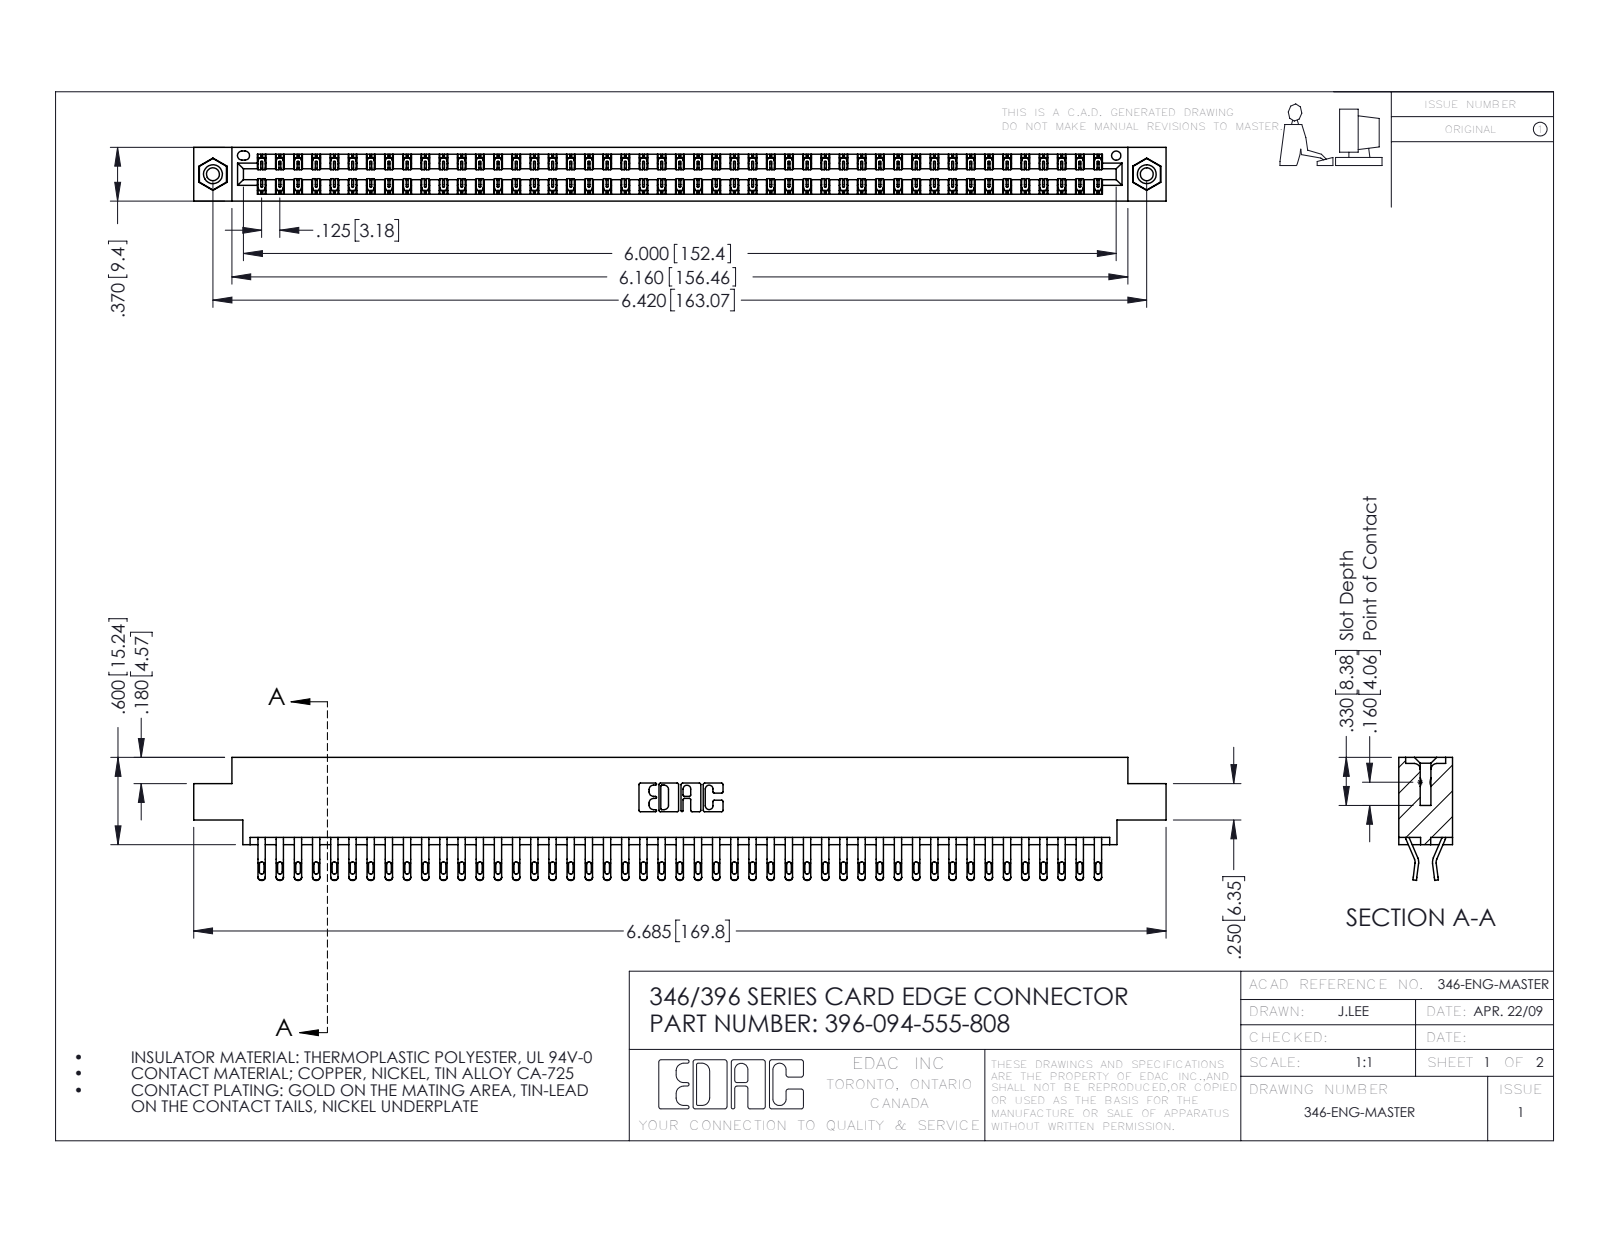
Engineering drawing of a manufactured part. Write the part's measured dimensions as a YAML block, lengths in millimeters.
part_name: "345-292-001_555 Tail; 345-250-001_345-250-003-102; 396-094-555-808; 346 Part_0.170 Offset - 0.156 Dia-TI"
step_written_by: "SolidWorks 2016 (CONFIG_CONTROL_DESIGN)"
units: millimeters
bodies: {solids: 97, faces: 5638, planar: 3214, cylindrical: 2408, other: 16}
overall_size: [169.8, 21.5, 9.4]
volume: 16710
surface_area: 24220
round_holes:
  - {diameter: 2.3, count: 2}
  - {diameter: 3.2, count: 2}
  - {diameter: 4, count: 2}
  - {diameter: 1.6, count: 1}
round_bosses_or_shafts:
  - {diameter: 3.9, count: 2}
partial_cylinders:
  - {radius: 0.4, count: 188}
  - {radius: 0.5, count: 188}
  - {radius: 0.2, count: 141}
  - {radius: 0.3, count: 22}
  - {radius: 0.2, count: 6}
  - {radius: 0.8, count: 6}
  - {radius: 0.7, count: 3}
  - {radius: 0.3, count: 2}
face_to_face_distances: [1.2, 8.2, 9.4, 6.4, 0.6, 1.8, 7.6, 7, 5.6, 3.8]
hole_center_spacings: [6.2, 157.8, 163.1]
